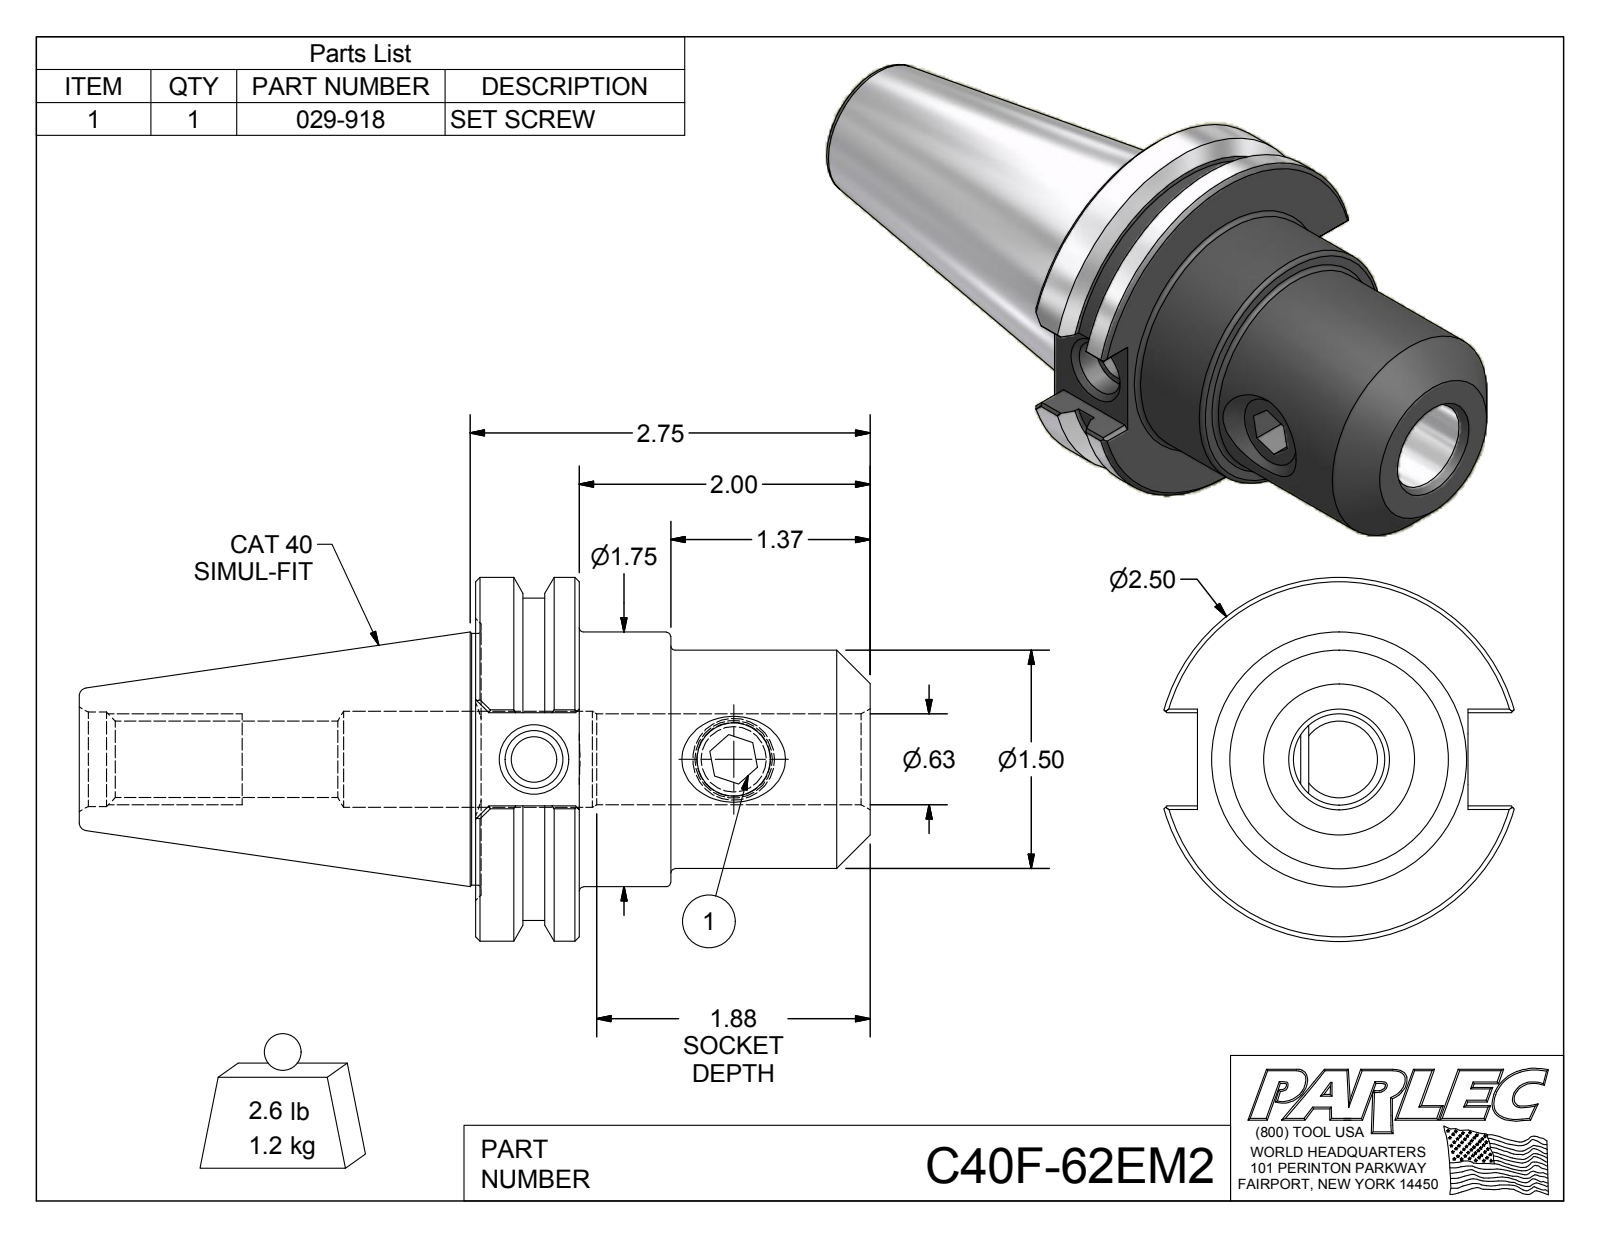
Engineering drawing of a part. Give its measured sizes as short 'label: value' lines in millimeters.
name: C40F-62EM2; C40F-62EM2-1; 029-918
written by: Autodesk Inventor 2012 (AUTOMOTIVE_DESIGN)
unit: mm
bodies: 2 solids, 90 faces (42 planar, 17 cylindrical, 31 other)
size: 138.1 × 63.5 × 61.1
volume: 151 900 mm³; area: 30 510 mm²
holes: 1× ⌀8, 1× ⌀10.1, 1× ⌀12.8, 1× ⌀13.4, 1× ⌀15.9, 1× ⌀16.5, 1× ⌀16.8
bosses: 1× ⌀63.5, 1× ⌀56.3, 1× ⌀44.5, 1× ⌀43.9, 1× ⌀38.1, 1× ⌀14.3
face distances: 18.1, 68.9, 50.8, 34.1, 16, 34.8, 47.2, 16.3, 0.9, 17.1
hole spacings: 34.8
